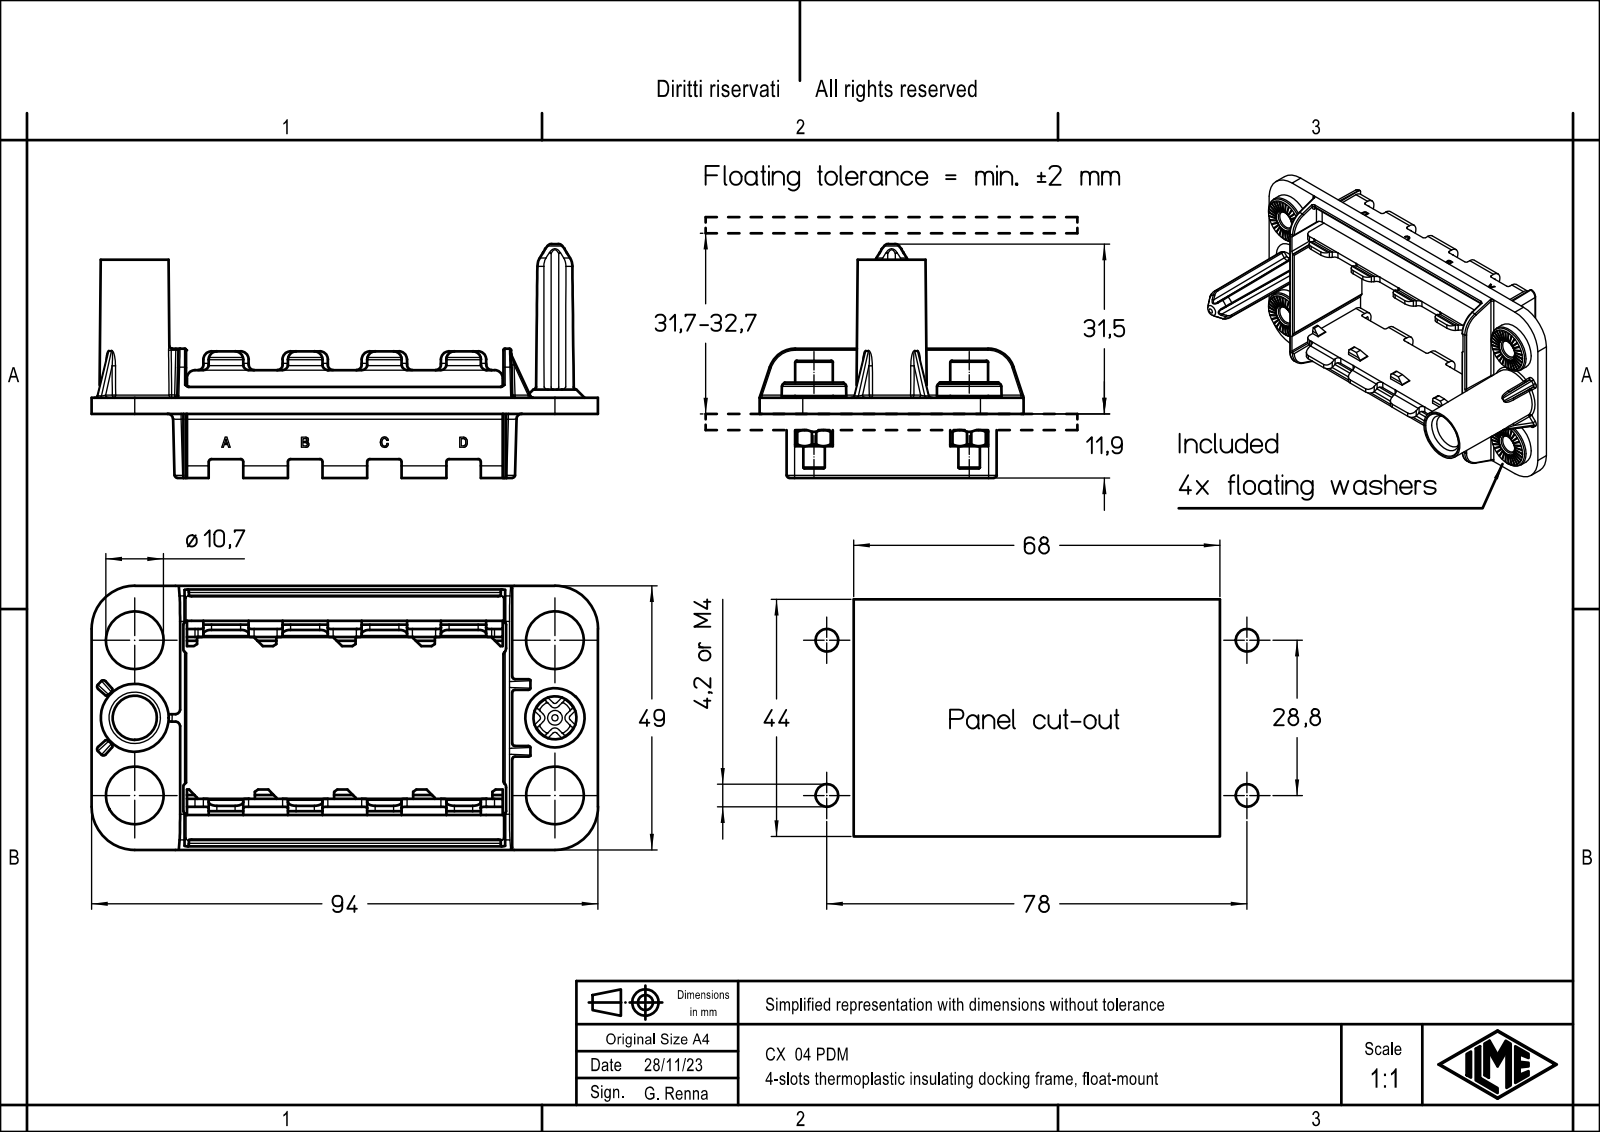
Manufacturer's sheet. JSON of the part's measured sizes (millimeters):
{"part_name": "CX 04 PDM", "step_written_by": "Creo Elements/Direct Modeling 20.1B 02-Apr-2019 (C) Parametric Technology GmbH (AUTOMOTIVE_DESIGN)", "units": "millimeters", "bodies": {"solids": 1, "faces": 519, "planar": 305, "cylindrical": 154, "other": 60}, "overall_size": [94, 49, 43.4], "volume_mm3": 18802, "surface_area_mm2": 21592, "round_holes": [[10.5, 2], [10.7, 2]], "partial_cylinders_radius": [[1.5, 22], [1, 21], [0.5, 16], [0.1, 15], [8, 4], [0.75, 2], [2, 2], [2.25, 2]], "face_to_face_distances": [1.5, 3, 34.5, 33, 31.5, 36, 4.5, 37.5, 30, 0.5], "hole_center_spacings": [28.8, 78, 83.15]}
